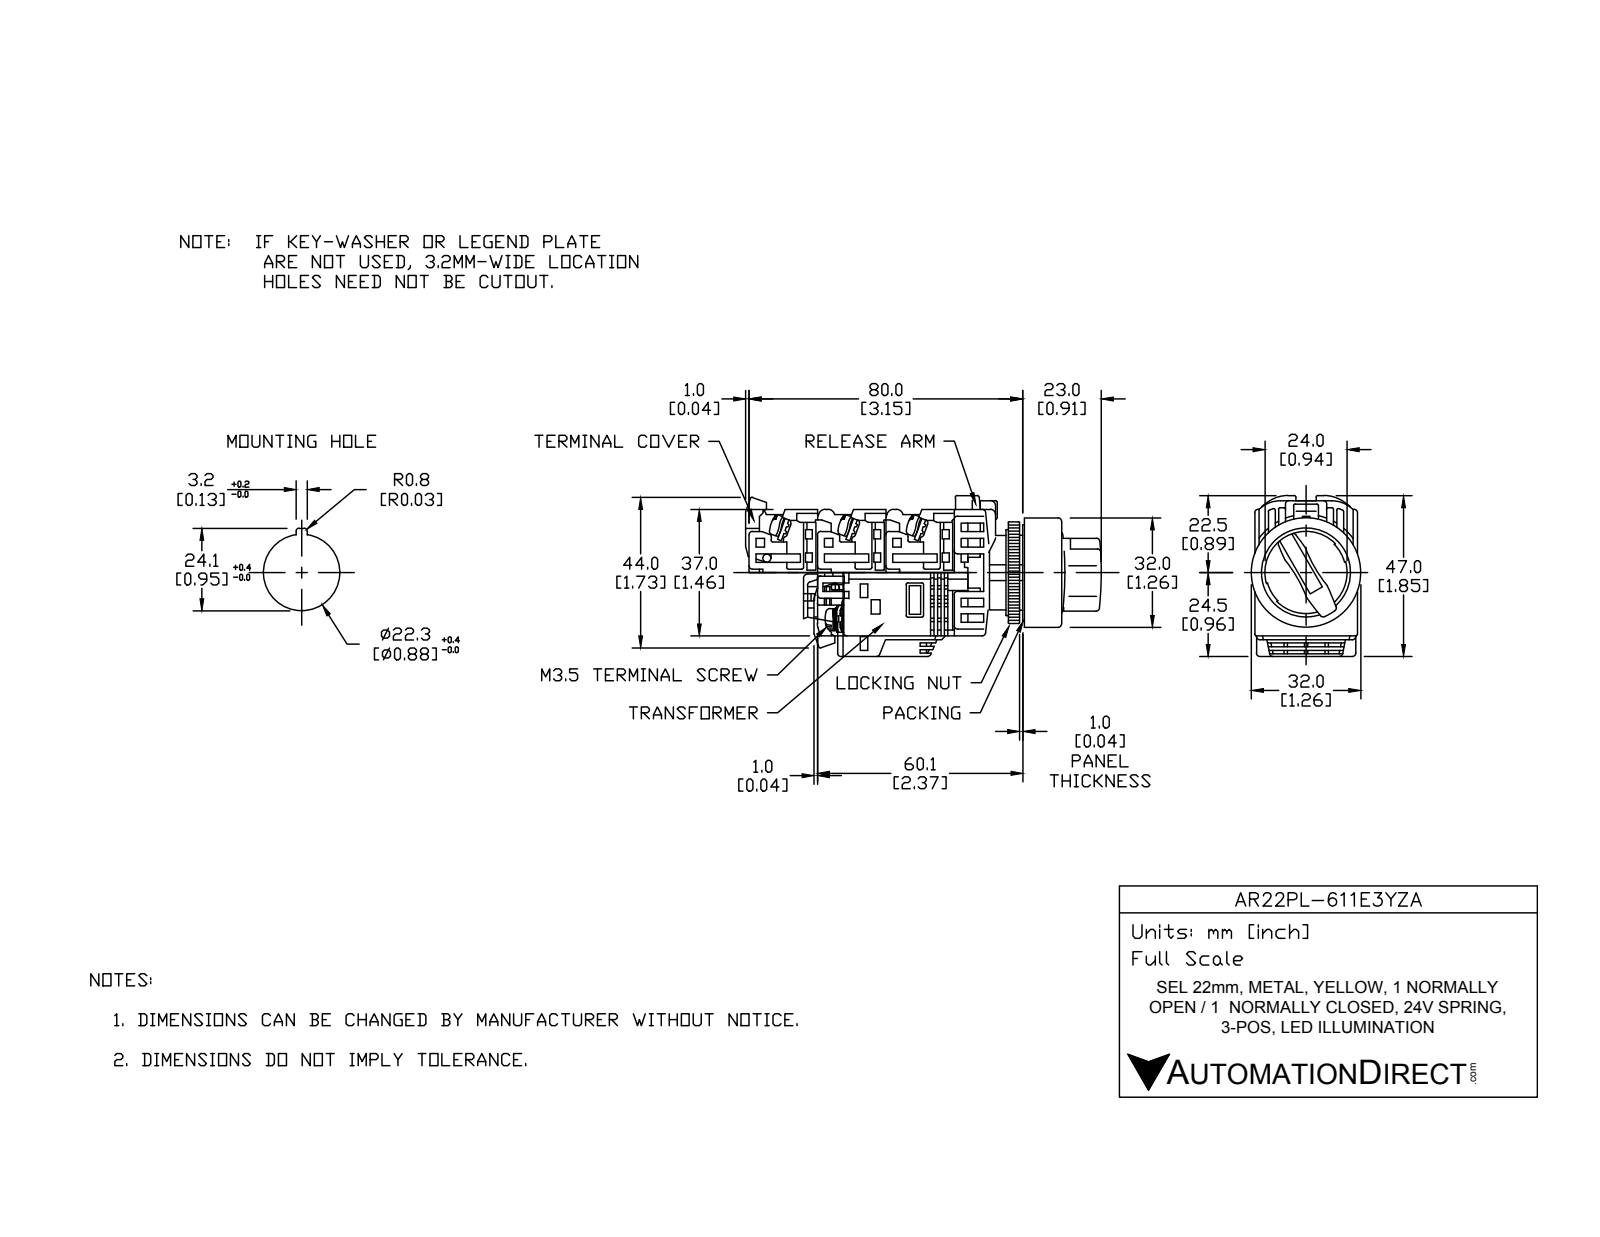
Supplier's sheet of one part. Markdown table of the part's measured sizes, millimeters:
| quantity | value |
| --- | --- |
| part name | AR22PL-611E3YZA |
| STEP written by | SolidWorks 2017 (AUTOMOTIVE_DESIGN) |
| units | millimeters |
| bodies | 23 solids, 556 faces (386 planar, 139 cylindrical, 31 other) |
| overall size | 84.5 × 43.81 × 32 |
| volume | 47 063 mm³ |
| surface area | 28 339 mm² |
| round holes (diameter × count) | 21.8 × 1, 22 × 1, 25 × 1, 31 × 1 |
| round bosses / shafts (diameter × count) | 5 × 6, 32 × 1, 30.5 × 1, 29.8 × 1, 24 × 1, 21.75 × 1, 17 × 1 |
| partial cylindrical surfaces (radius × count) | 0.5 × 48, 1.75 × 8, 1 × 6, 5 × 4, 4 × 2, 12 × 1, 16.59 × 1, 17.59 × 1 |
| main face-to-face distances | 1, 20, 18, 3, 29, 28.5, 48.5, 2, 10, 0.5 |
